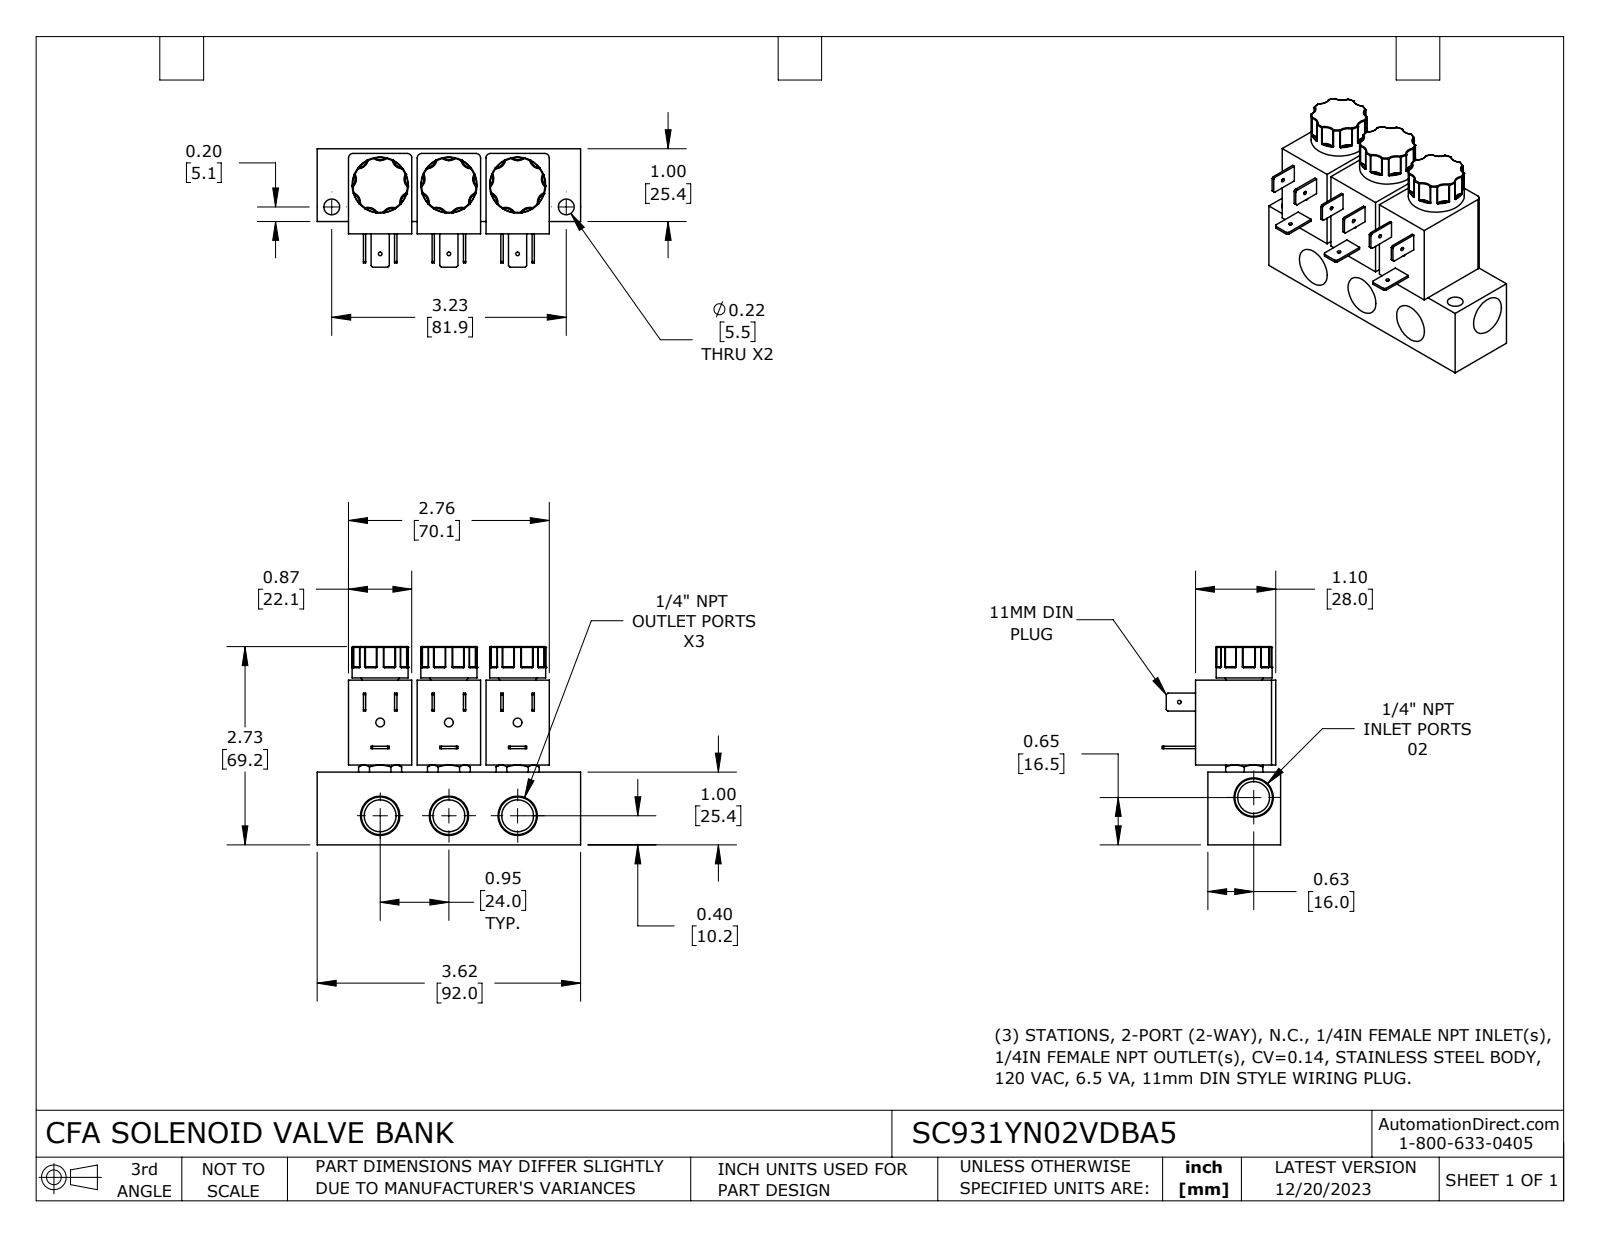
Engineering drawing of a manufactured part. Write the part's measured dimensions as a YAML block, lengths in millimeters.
part_name: "SC931YN02VDBA5"
step_written_by: "SolidWorks 2023 (CONFIG_CONTROL_DESIGN)"
units: millimeters
bodies: {solids: 1, faces: 657, planar: 146, cylindrical: 140, other: 371}
overall_size: [92, 69.2, 41.3]
volume: 114800
surface_area: 30850
round_holes:
  - {diameter: 1.3, count: 4}
  - {diameter: 11.1, count: 4}
  - {diameter: 3, count: 3}
  - {diameter: 5.5, count: 2}
round_bosses_or_shafts:
  - {diameter: 19.6, count: 3}
partial_cylinders:
  - {radius: 0.3, count: 54}
  - {radius: 3.4, count: 25}
  - {radius: 1.5, count: 6}
  - {radius: 3.4, count: 2}
face_to_face_distances: [25.4, 24, 22.1, 29.7, 4.3, 1.7, 23.7, 28, 48, 46.1]
hole_center_spacings: [24, 40.5, 32.6, 48, 58, 23.6, 23.6, 42.2]
